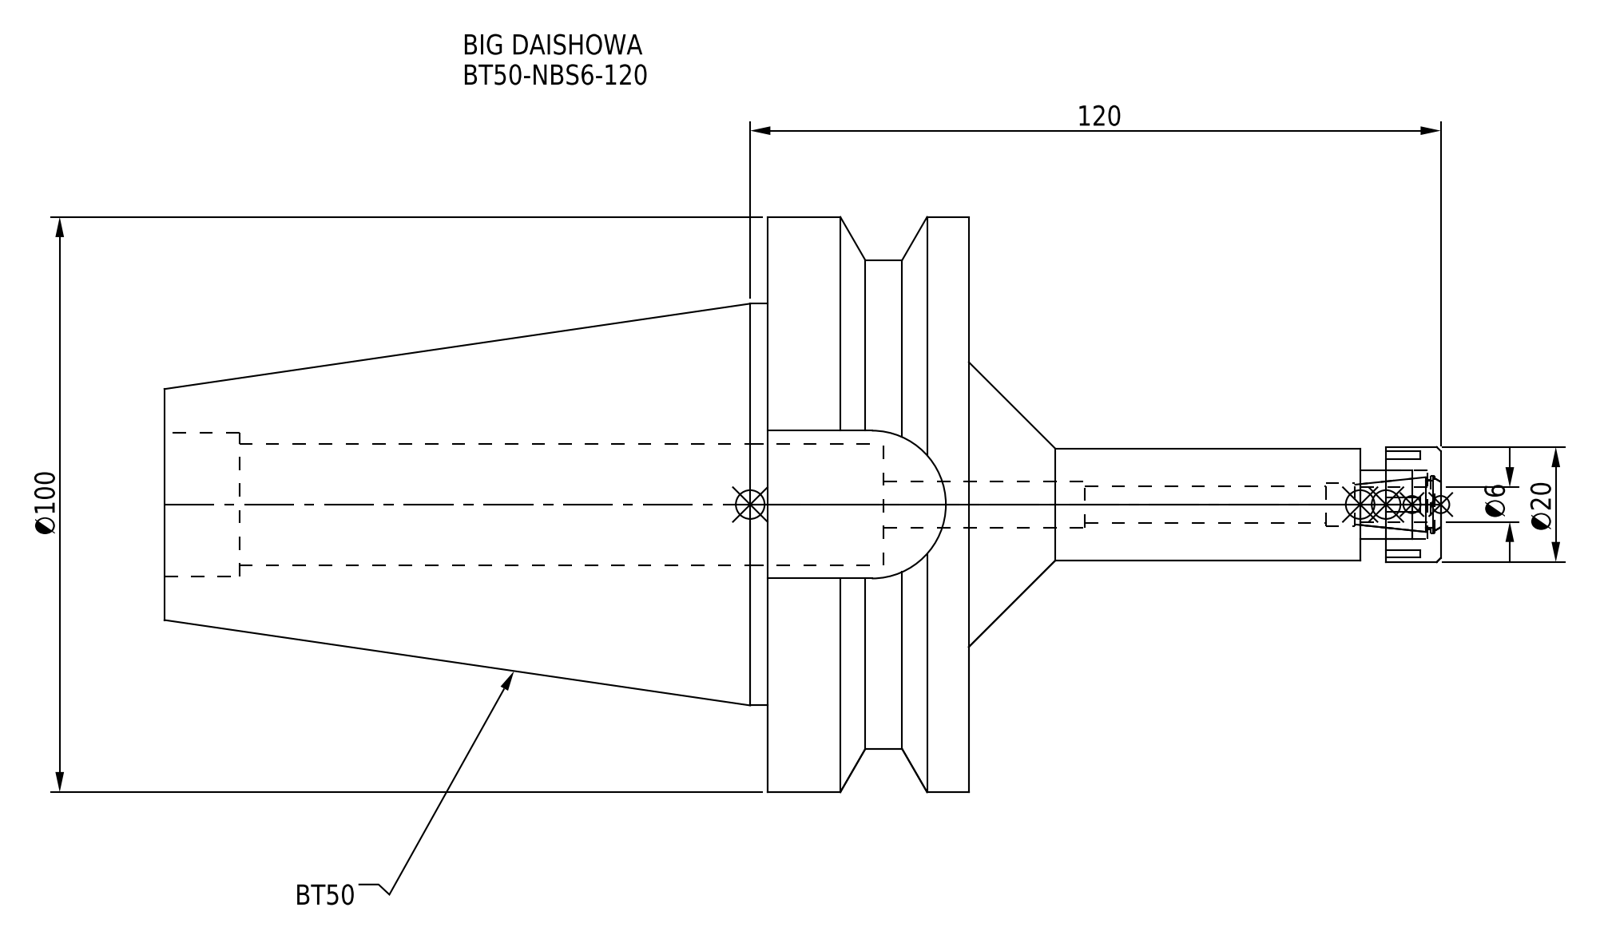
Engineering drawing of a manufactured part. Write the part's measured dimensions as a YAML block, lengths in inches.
part_name: "BT50-NBS6-120.stp; NBN6_1.stp; BT50-NBS6-120-FreeParts; BT50NB06120-060_ASM.stp (+3 more)"
step_written_by: "SolidWorks 2019 (CONFIG_CONTROL_DESIGN)"
units: inches
bodies: {solids: 2, faces: 93, planar: 45, cylindrical: 34, other: 14}
overall_size: [8.732, 3.937, 3.937]
volume: 29.16
surface_area: 95.26
round_holes:
  - {diameter: 0.252, count: 1}
  - {diameter: 0.295, count: 1}
  - {diameter: 0.315, count: 1}
  - {diameter: 0.335, count: 1}
  - {diameter: 0.394, count: 1}
  - {diameter: 0.472, count: 1}
  - {diameter: 0.835, count: 1}
  - {diameter: 0.984, count: 1}
round_bosses_or_shafts:
  - {diameter: 3.937, count: 1}
  - {diameter: 3.346, count: 1}
  - {diameter: 2.75, count: 1}
  - {diameter: 0.787, count: 1}
  - {diameter: 0.768, count: 1}
partial_cylinders:
  - {radius: 0.506, count: 1}
face_to_face_distances: [1.378, 5.504, 4.126, 2.787, 1.012, 0.795, 0.583, 4.921, 0.177, 3.228]
